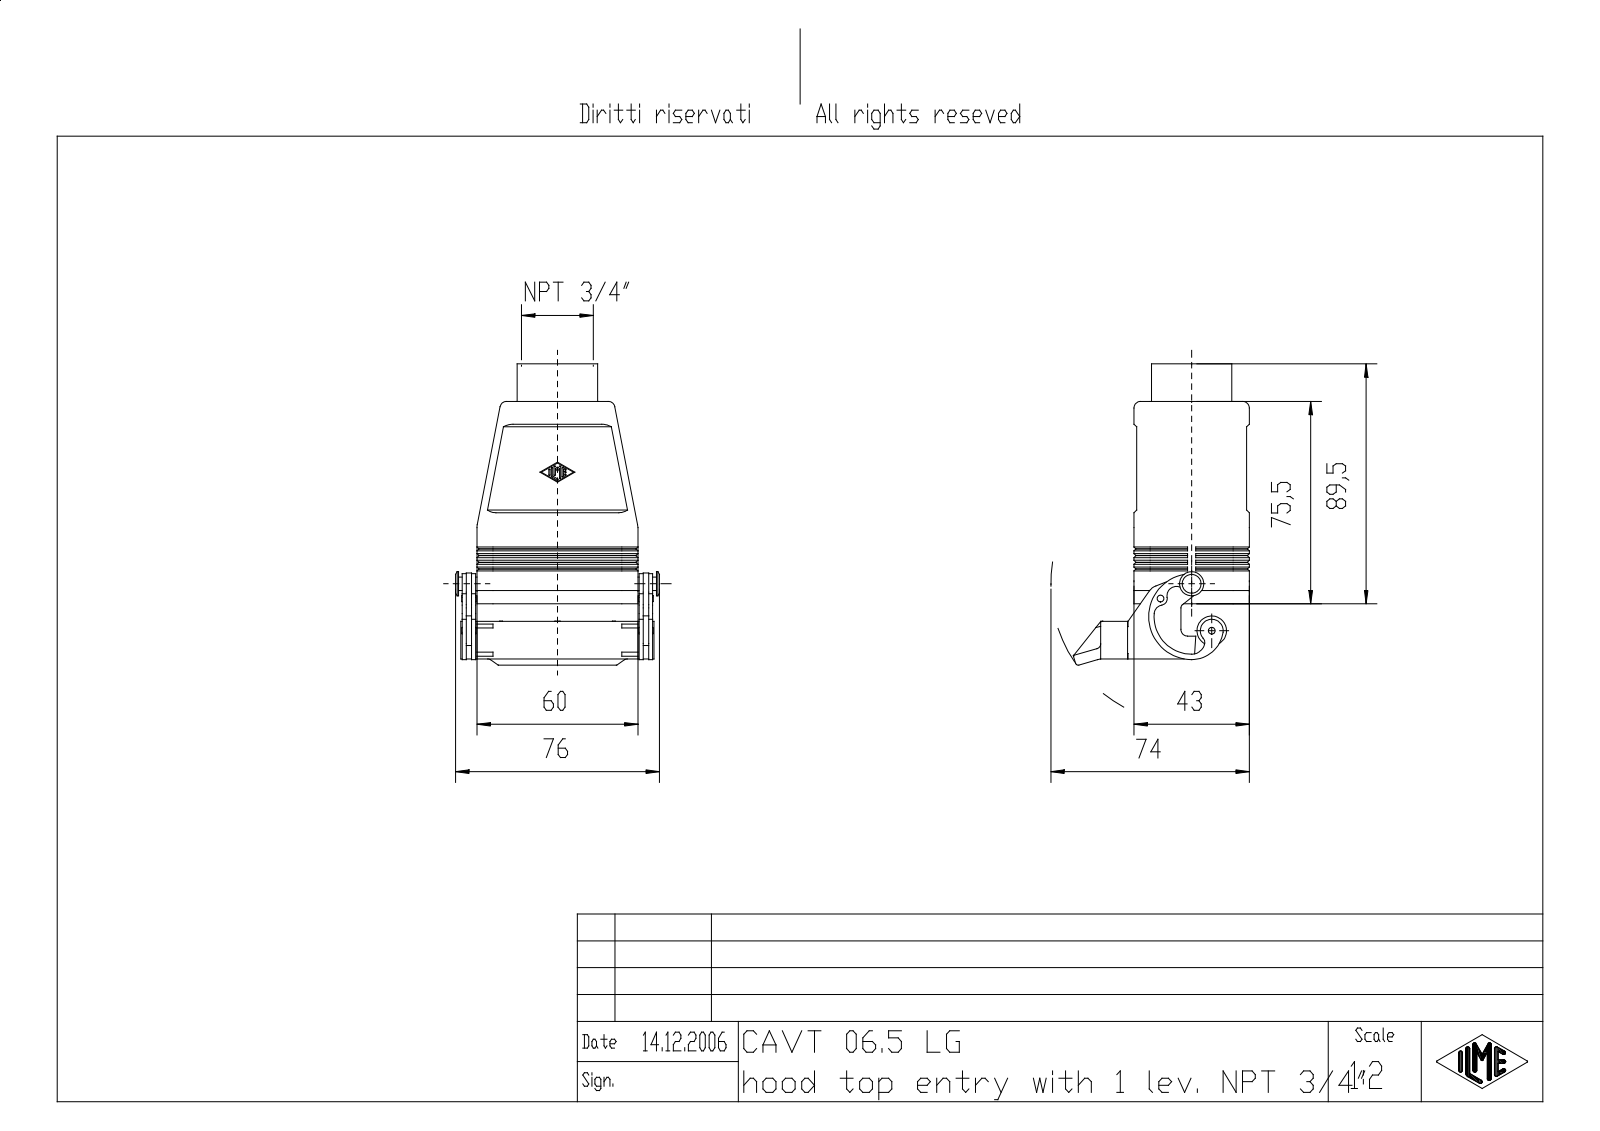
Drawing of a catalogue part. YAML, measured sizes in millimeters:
part_name: "MSBO10619"
step_written_by: "Creo Elements/Direct Modeling 18.0B 02-Dec-2011 (C) Parametric Technology GmbH (AUTOMOTIVE_DESIGN)"
units: millimeters
bodies: {solids: 1, faces: 537, planar: 299, cylindrical: 168, other: 70}
overall_size: [112.34, 76, 65.59]
volume: 74630
surface_area: 41569
round_holes:
  - {diameter: 2.46, count: 4}
  - {diameter: 4, count: 4}
  - {diameter: 2.5, count: 1}
  - {diameter: 24.78, count: 1}
round_bosses_or_shafts:
  - {diameter: 30, count: 1}
  - {diameter: 25.78, count: 1}
  - {diameter: 11, count: 1}
  - {diameter: 9, count: 1}
  - {diameter: 5, count: 1}
  - {diameter: 2, count: 1}
partial_cylinders:
  - {radius: 0.25, count: 14}
  - {radius: 6, count: 10}
  - {radius: 2, count: 7}
  - {radius: 2.5, count: 7}
  - {radius: 3, count: 4}
  - {radius: 5.3, count: 4}
  - {radius: 3.5, count: 2}
  - {radius: 5, count: 2}
face_to_face_distances: [4, 38, 39, 1, 3, 42, 35, 2, 60, 11]
hole_center_spacings: [25.81, 27, 44, 51.62]
